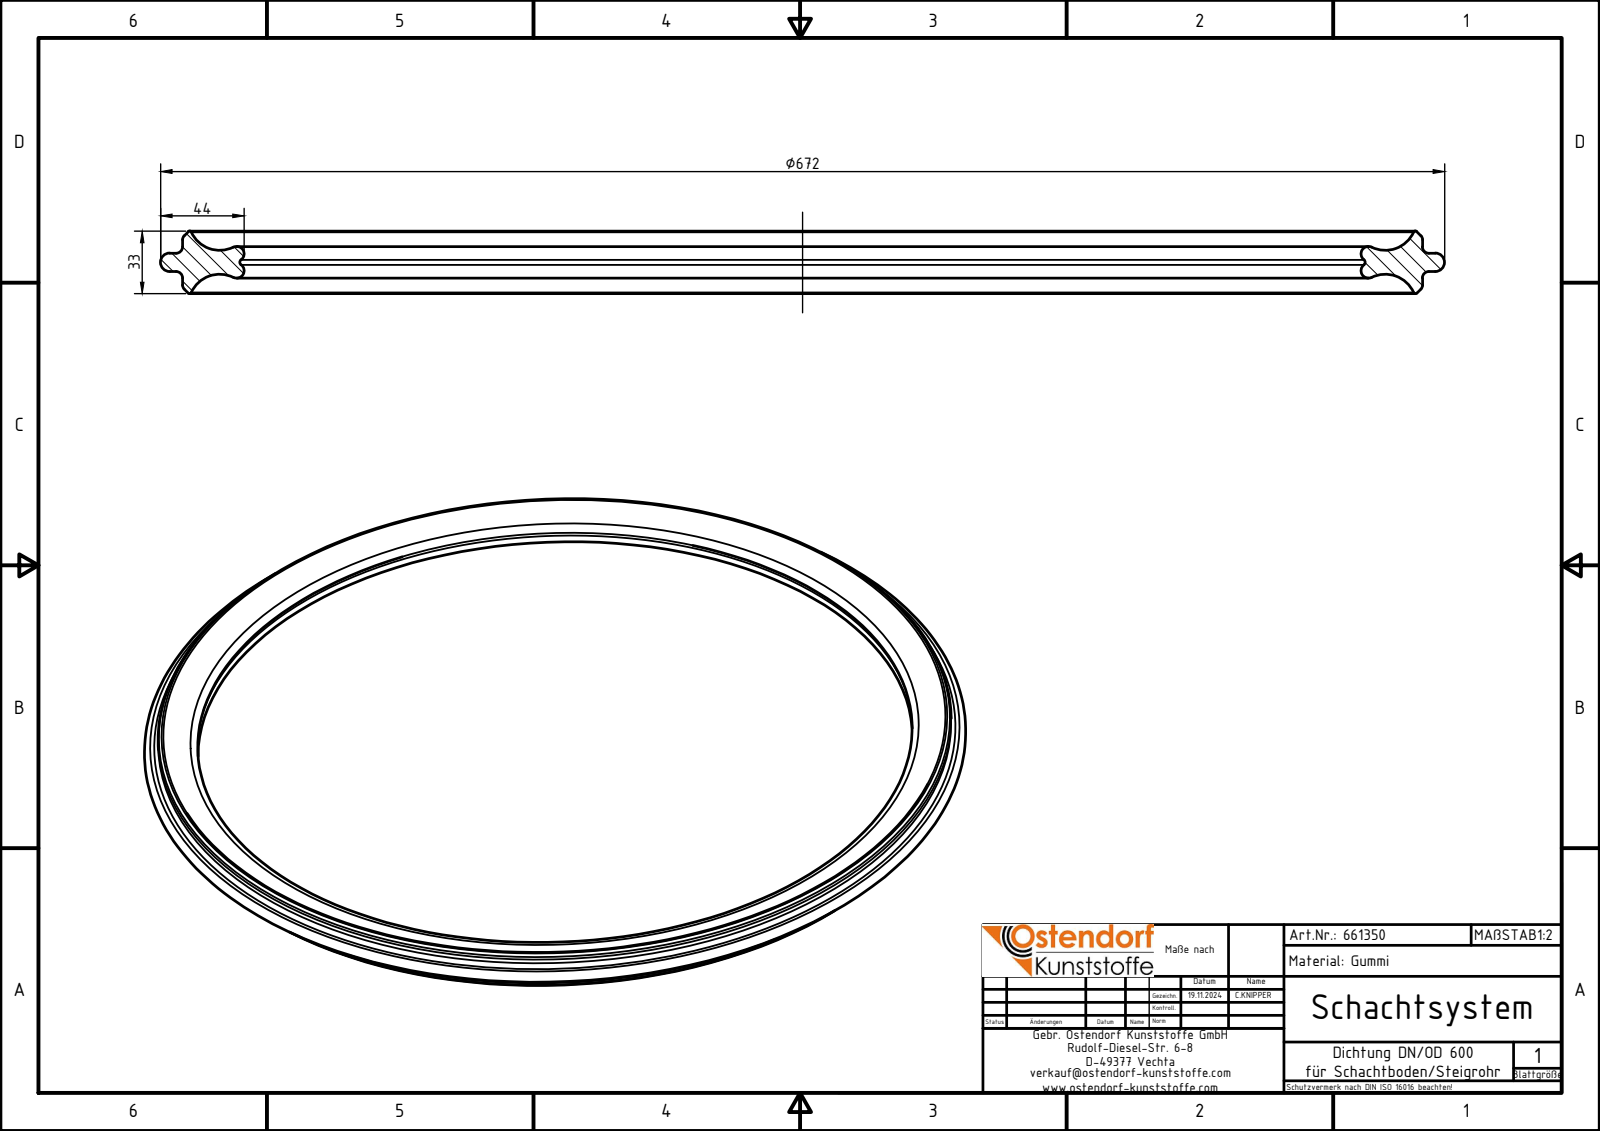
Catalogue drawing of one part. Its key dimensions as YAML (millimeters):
part_name: "661350z"
step_written_by: "Autodesk Inventor 2024 (AUTOMOTIVE_DESIGN)"
units: millimeters
bodies: {solids: 1, faces: 18, planar: 2, cylindrical: 2, other: 14}
overall_size: [672, 672, 32.65]
volume: 1342000
surface_area: 260790
round_bosses_or_shafts:
  - {diameter: 648.91, count: 1}
face_to_face_distances: [9.62]
